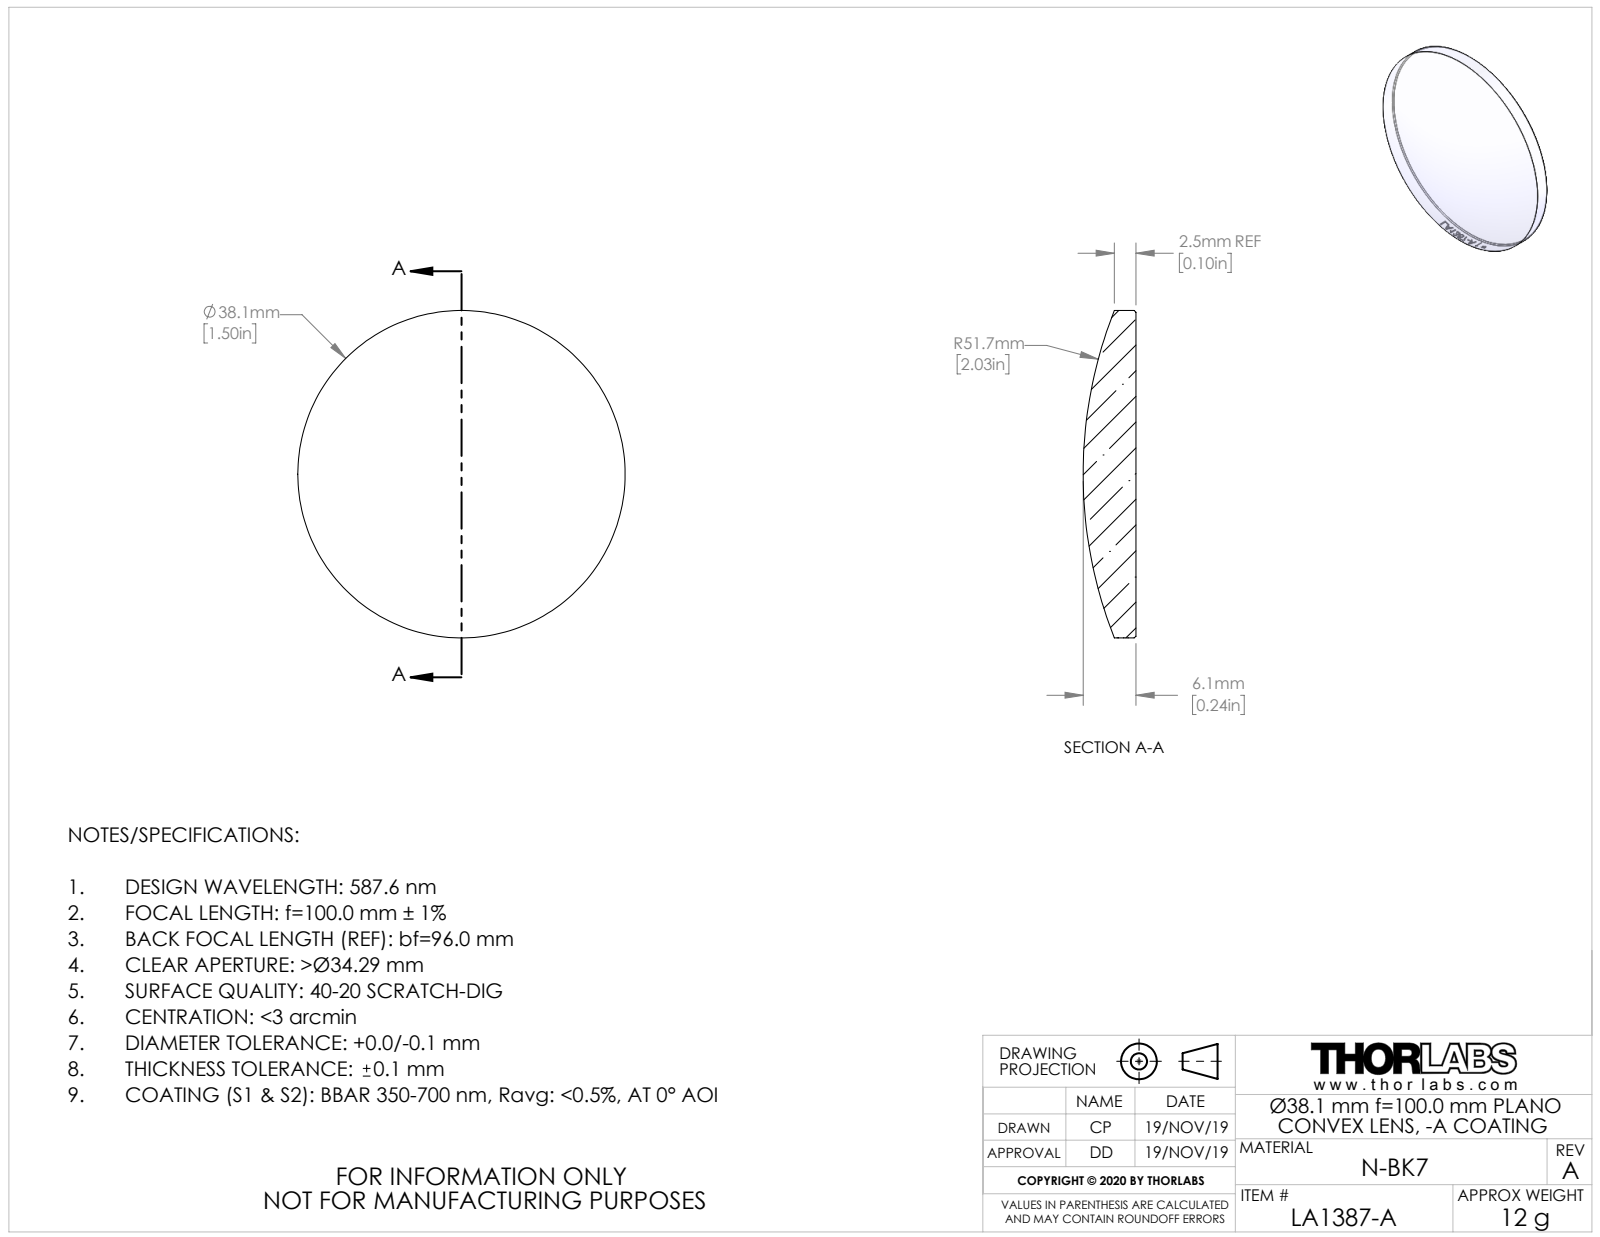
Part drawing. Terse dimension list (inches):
name: TTN200707-E0W
written by: SolidWorks 2018 (CONFIG_CONTROL_DESIGN)
unit: in
bodies: 1 solid, 23 faces (1 planar, 18 cylindrical, 4 other)
size: 1.5 × 1.5 × 0.242
volume: 0.302 in³; area: 4.041 in²
bosses: 1× ⌀1.5
